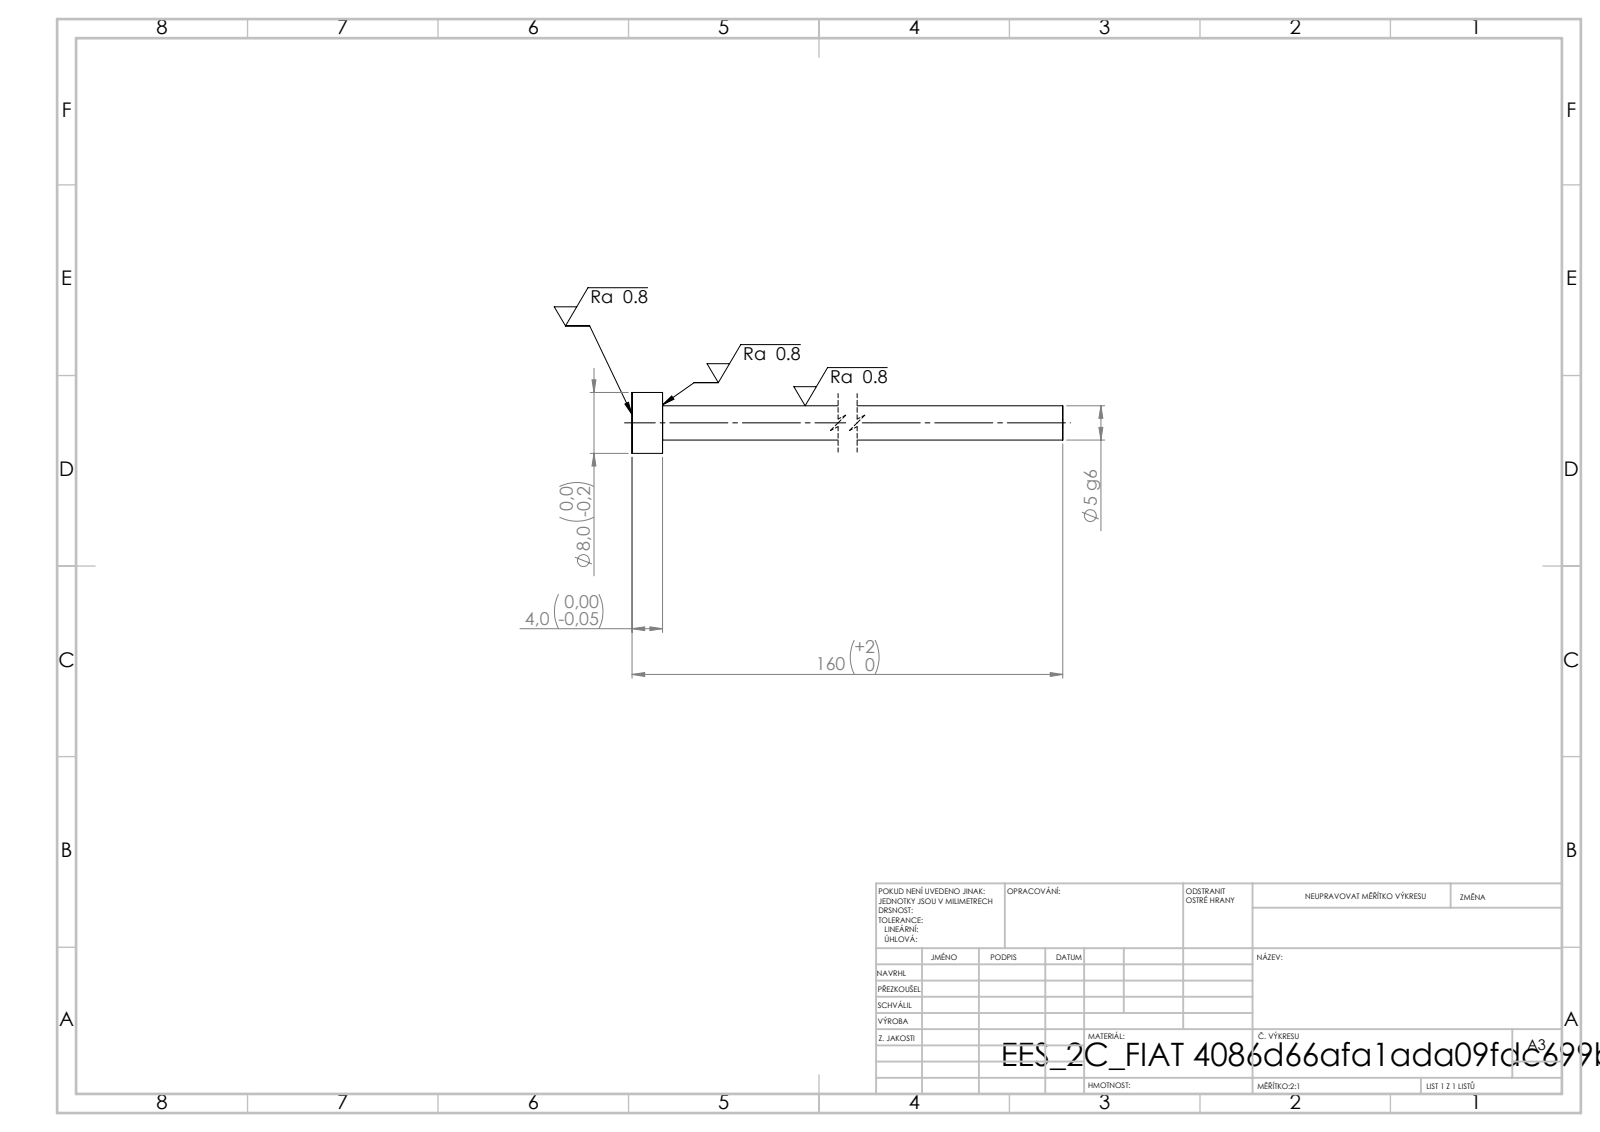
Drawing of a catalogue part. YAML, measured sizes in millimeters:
step_written_by: "SolidWorks 2019 (CONFIG_CONTROL_DESIGN)"
units: millimeters
bodies: {solids: 1, faces: 7, planar: 3, cylindrical: 4, other: 0}
overall_size: [160, 8, 8]
volume: 2682
surface_area: 2406
round_bosses_or_shafts:
  - {diameter: 8, count: 1}
  - {diameter: 4.5, count: 1}
face_to_face_distances: [4, 160, 156]
